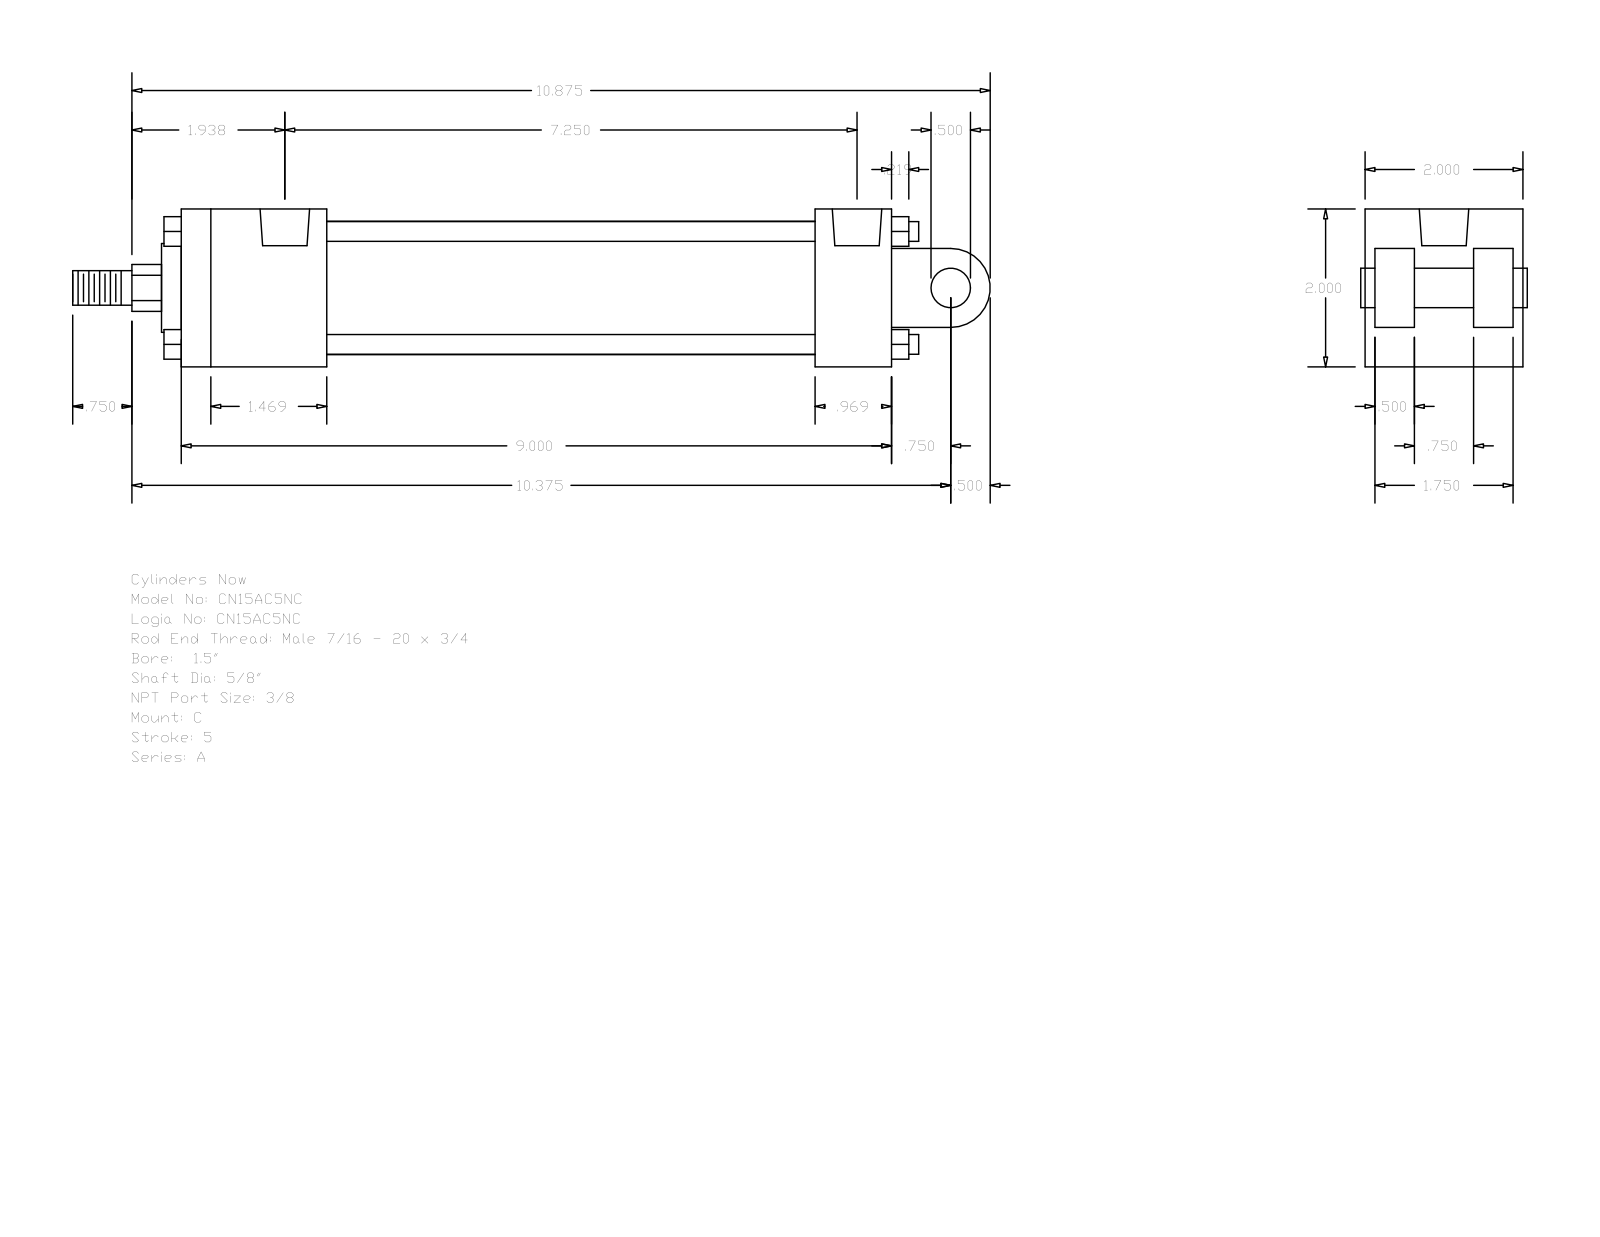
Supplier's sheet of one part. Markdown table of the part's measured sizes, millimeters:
| quantity | value |
| --- | --- |
| part name | A_C__0150_0.625 |
| STEP written by | GSSL Pune (CONFIG_CONTROL_DESIGN) |
| units | millimeters |
| bodies | 0 solids, 135 faces (102 planar, 33 cylindrical, 0 other) |
| overall size | 295.27 × 50.8 × 50.8 |
| round holes (diameter × count) | 5.56 × 4, 15.93 × 2 |
| round bosses / shafts (diameter × count) | 6.35 × 4, 42.93 × 1, 28.57 × 1, 15.88 × 1, 12.7 × 1, 11.11 × 1 |
| partial cylindrical surfaces (radius × count) | 7.54 × 1, 12.7 × 1 |
| main face-to-face distances | 50.8, 12.7, 228.59, 34.93, 3.17, 15.87, 47.63, 31.76, 203.99, 24.6 |
| hole center spacings | 3.97, 176.21, 180.18, 184.15 |
